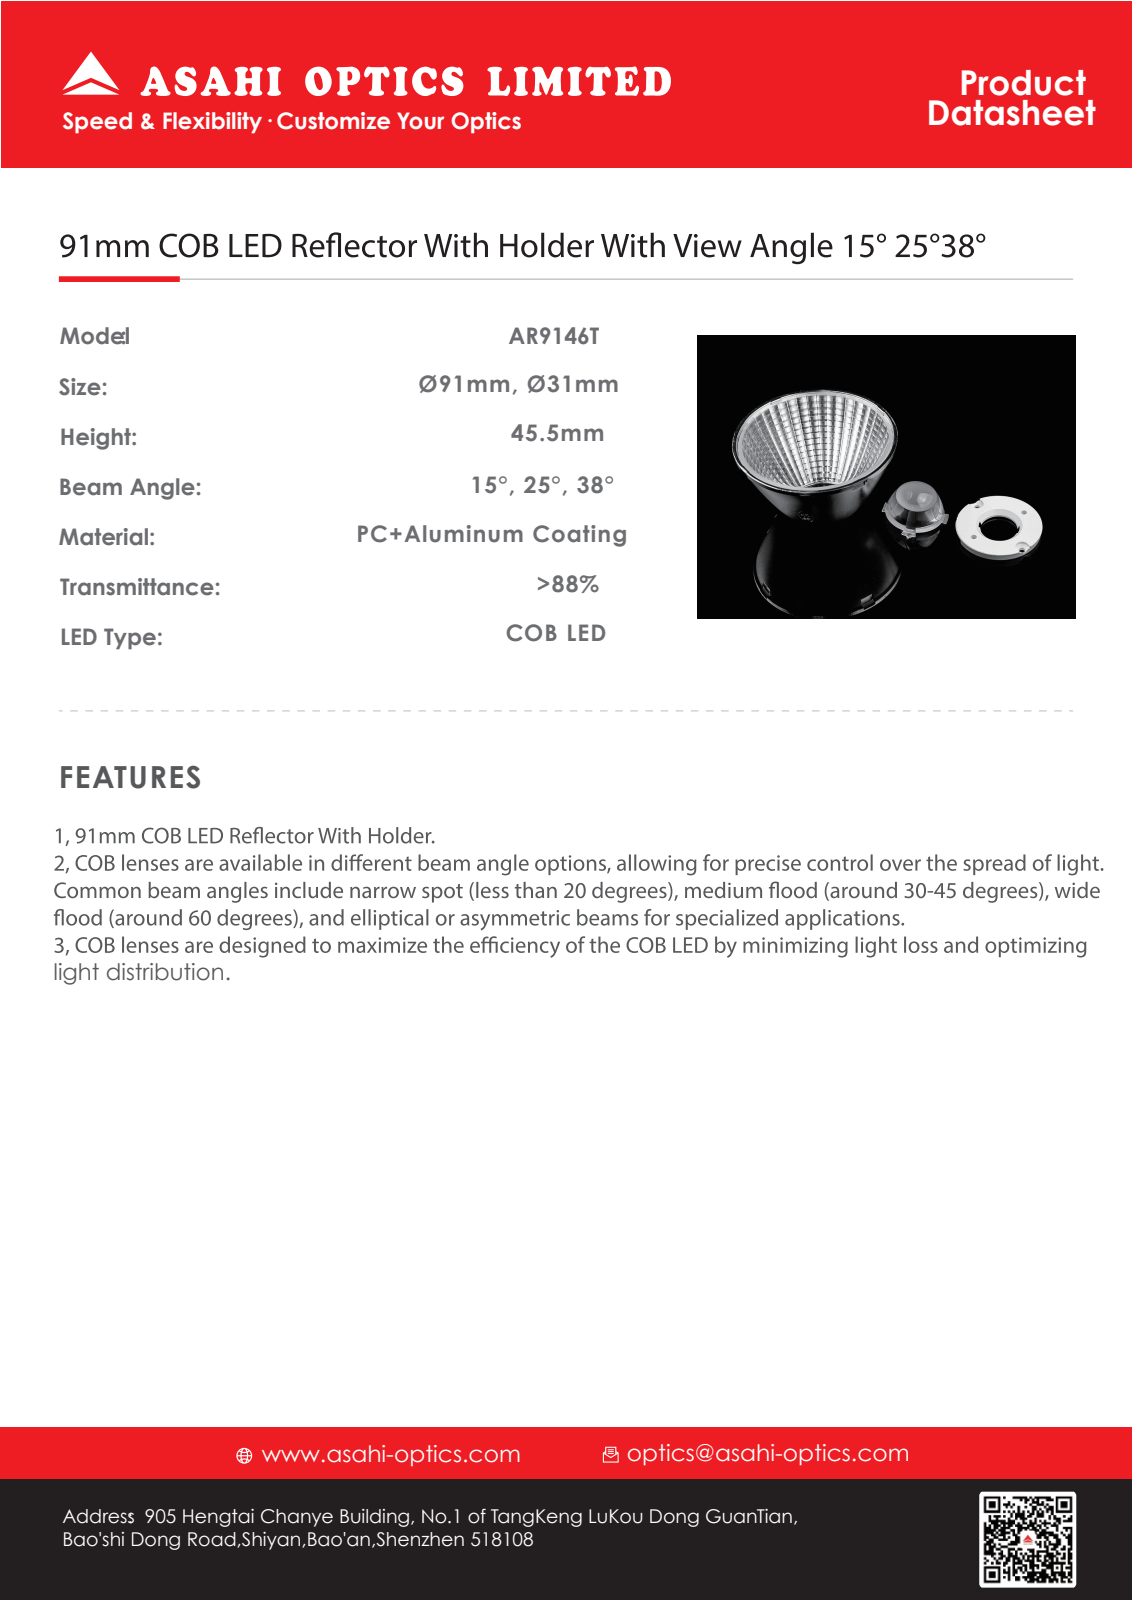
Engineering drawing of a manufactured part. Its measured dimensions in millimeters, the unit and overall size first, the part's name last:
Units: millimetres
Overall size (bounding box): 91 × 91 × 45.5
Round holes (diameter × count): ⌀31 ×1, ⌀89 ×1
Round bosses / shafts (diameter × count): ⌀91 ×1
Partial cylindrical surfaces — rounded edges, fillets, slot ends (radius × count): R44 ×1
Main face-to-face distances: 1, 43.5, 42.5, 44.5, 45.5, 2
Volume: 23 879 mm³ · Surface area: 23 931 mm²
Bodies: 1 solid, 220 faces (28 planar, 14 cylindrical, 178 other)
Part name (STEP PRODUCT): 9145T
STEP written by: SolidWorks 2016 (AUTOMOTIVE_DESIGN)
